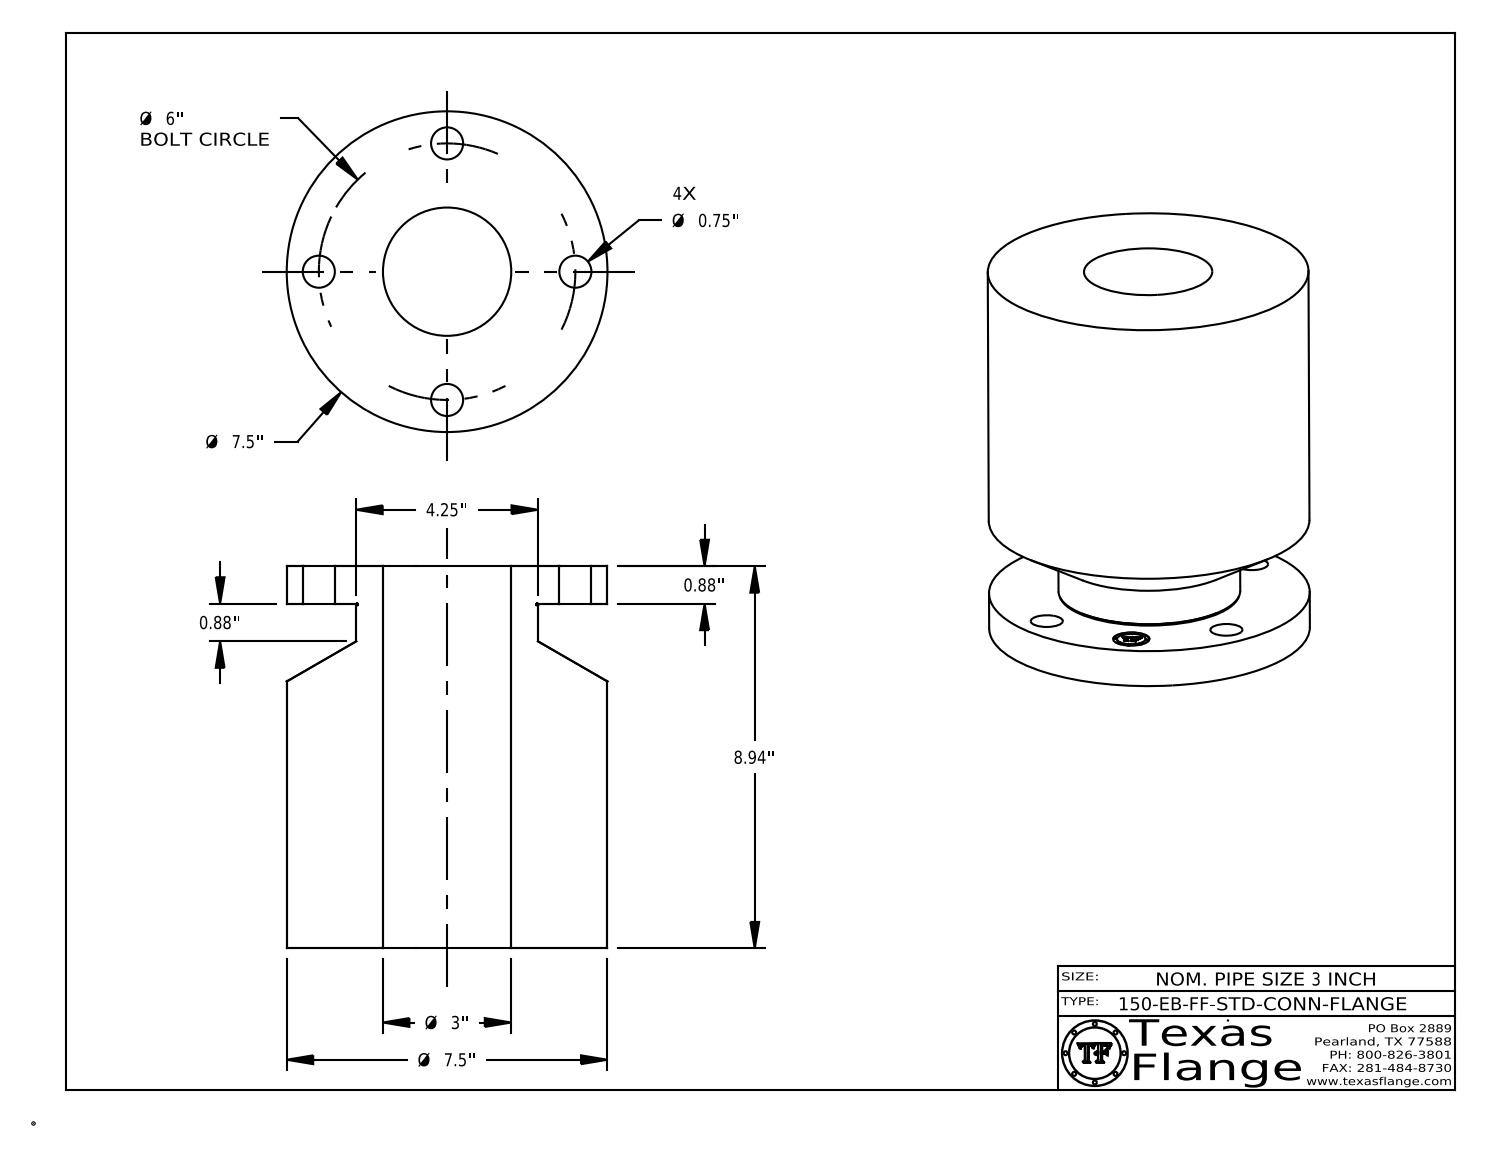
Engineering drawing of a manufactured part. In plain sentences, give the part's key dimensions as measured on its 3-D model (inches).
The part is named "3-150-EB-FF-STD-CONN-FLANGE". Its 3-D file was written by "CATIA V5 STEP AP214 (AUTOMOTIVE_DESIGN)". It is 1 solid with 410 faces: 368 planar, 36 cylindrical and 6 other. Overall it measures 8.938 by 7.5 by 7.5 inches. Its volume is 288.3 cubic inches and its surface area 407.9 square inches. Round holes: 4 of diameter 0.75, 1 of diameter 0.85, 1 of diameter 3. Round bosses or shafts: 8 of diameter 0.051, 1 of diameter 7.5, 1 of diameter 4.25, 1 of diameter 0.67. The main face-to-face distances are 8.937, 0.878, 8.06, 0.872, 8.065, 0.254, 0.248, 0.016, 0.046, 0.165. The hole center spacings are 3, 4.243, 2.296, 5.543, 6.
